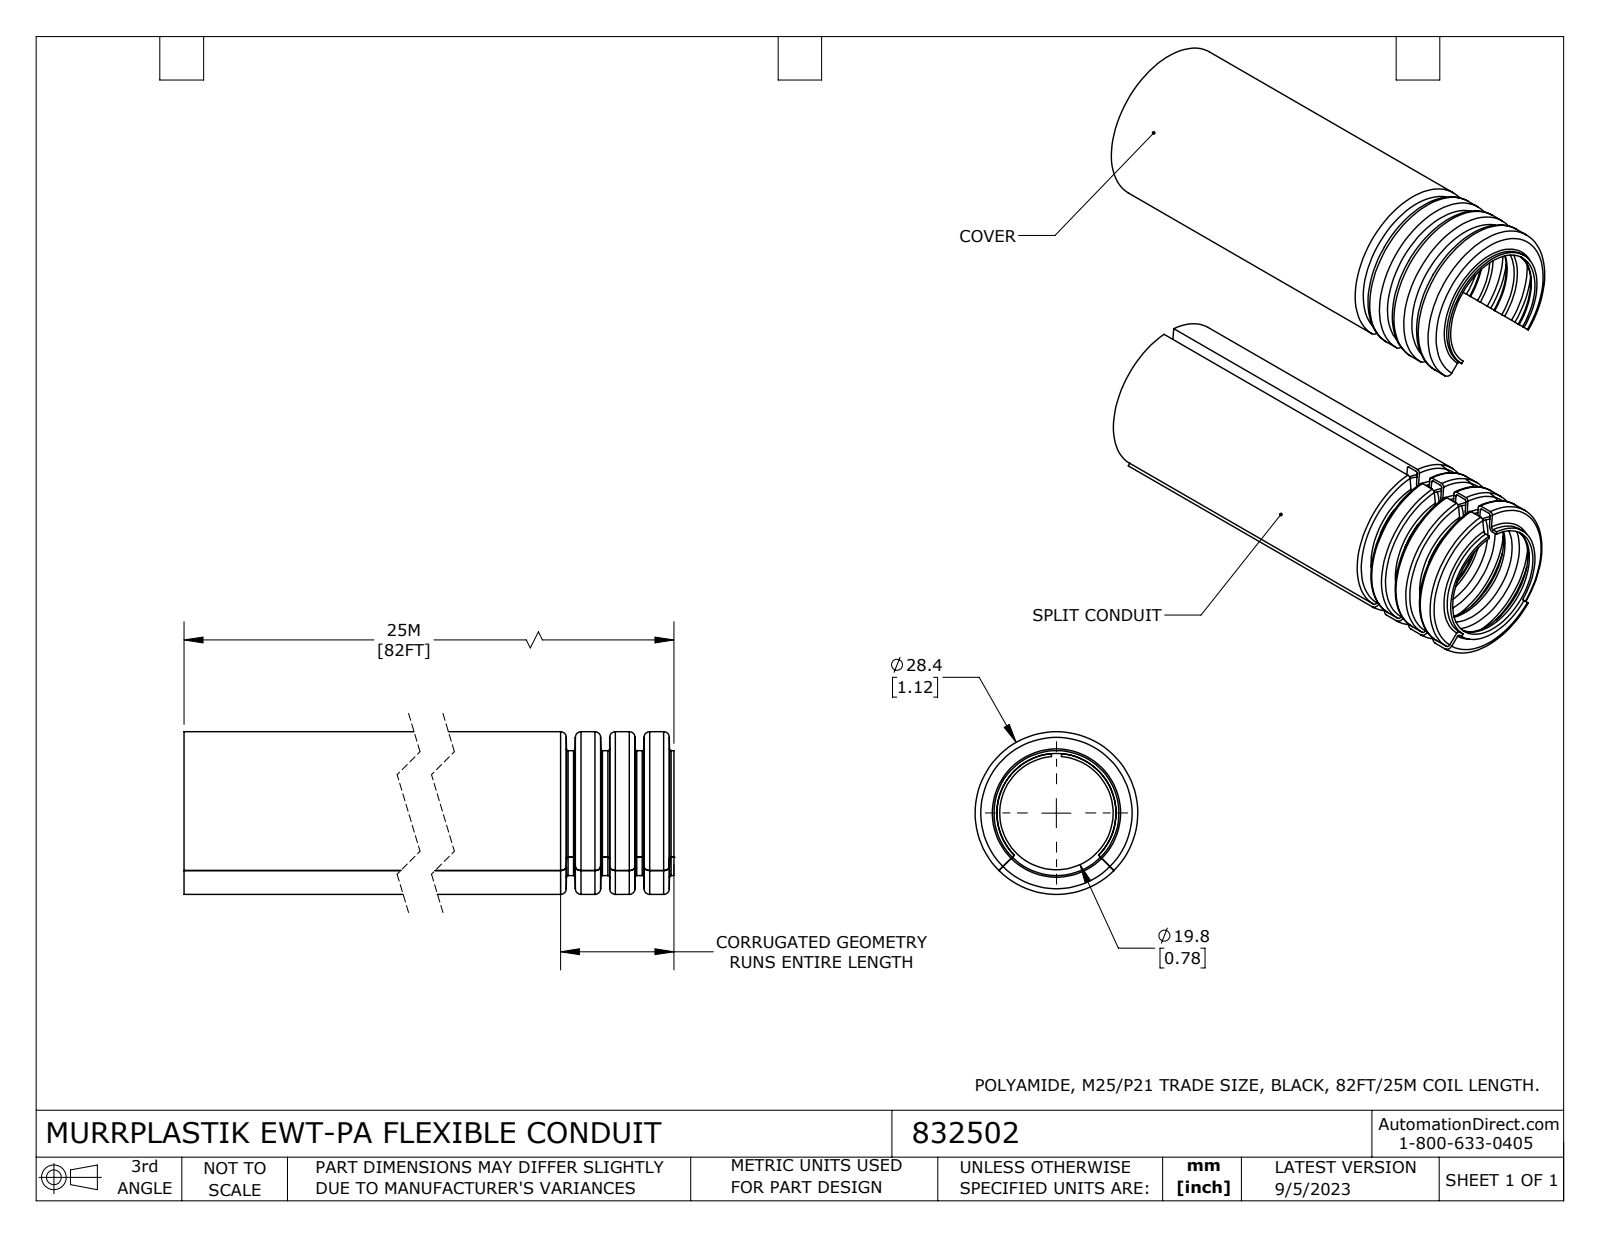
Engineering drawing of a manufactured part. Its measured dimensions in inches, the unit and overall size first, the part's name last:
Units: inches
Overall size (bounding box): 3.15 × 1.118 × 1.118
Round holes (diameter × count): ⌀0.78 ×1, ⌀1.039 ×1
Round bosses / shafts (diameter × count): ⌀1.118 ×1, ⌀0.858 ×1
Partial cylindrical surfaces — rounded edges, fillets, slot ends (radius × count): R0.409 ×1, R0.539 ×1
Main face-to-face distances: 3.15
Volume: 1.317 in³ · Surface area: 43.86 in²
Bodies: 2 solids, 330 faces (10 planar, 107 cylindrical, 213 other)
Part name (STEP PRODUCT): 832502
STEP written by: SolidWorks 2021 (CONFIG_CONTROL_DESIGN)
